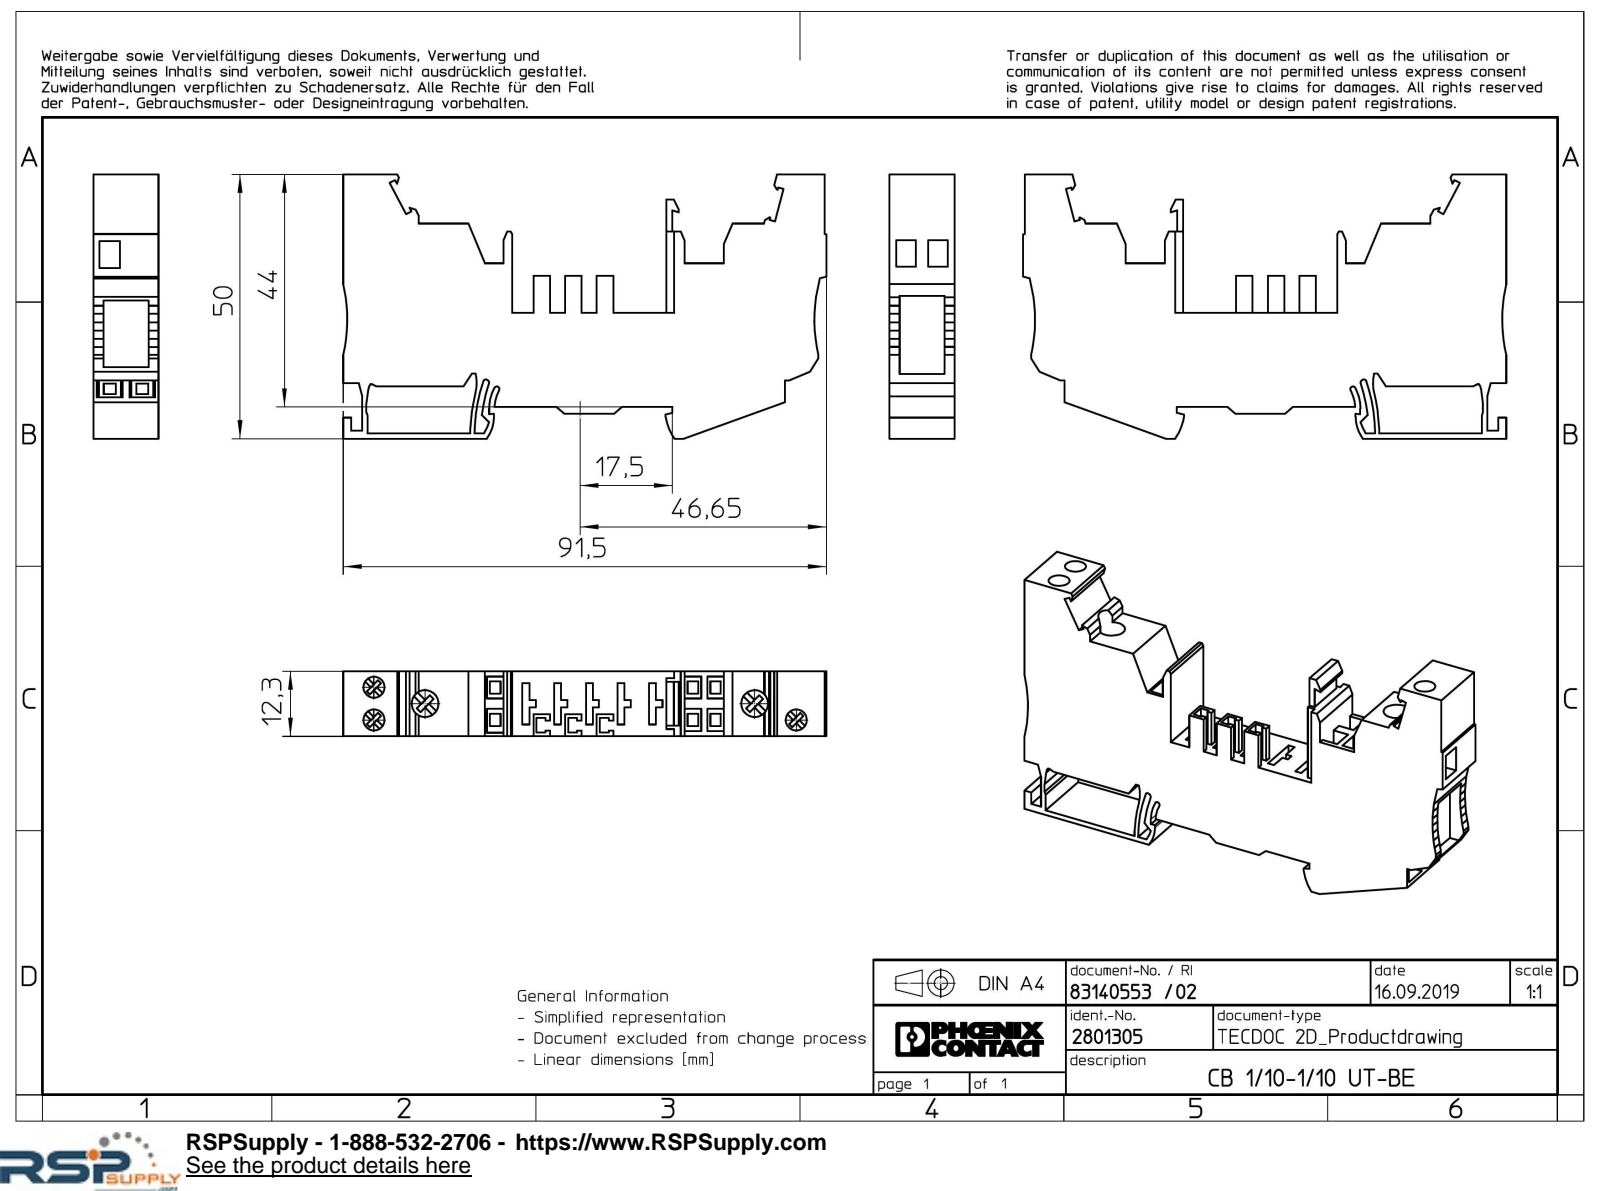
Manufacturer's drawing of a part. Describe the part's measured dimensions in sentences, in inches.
The part is named "CB_1_10_1_10_UT_BE-select". Its 3-D file was written by "Creo Elements/Direct Modeling 20.1A 29-Sep-2018 (C) Parametric Technology GmbH (AUTOMOTIVE_DESIGN)". It is 1 solid with 408 faces: 386 planar, 22 cylindrical and 0 other. Overall it measures 3.602 by 1.969 by 0.484 inches. Its volume is 1.864 cubic inches and its surface area 22.52 square inches. Round holes: 3 of diameter 0.157, 2 of diameter 0.201. Partial cylindrical surfaces (rounded edges, fillets, slot ends): 3 of radius 0.02, 1 of radius 0.276, 1 of radius 0.287, 1 of radius 0.295, 1 of radius 0.327, 1 of radius 0.335, 1 of radius 0.374, 1 of radius 1.187. The main face-to-face distances are 0.484, 0.039, 0.197, 0.124, 0.177, 1.579, 0.236, 0.281, 0.242, 0.937. The hole center spacings are 0.401, 2.842, 0.244, 0.334, 2.457, 2.77, 3.15, 3.159.
